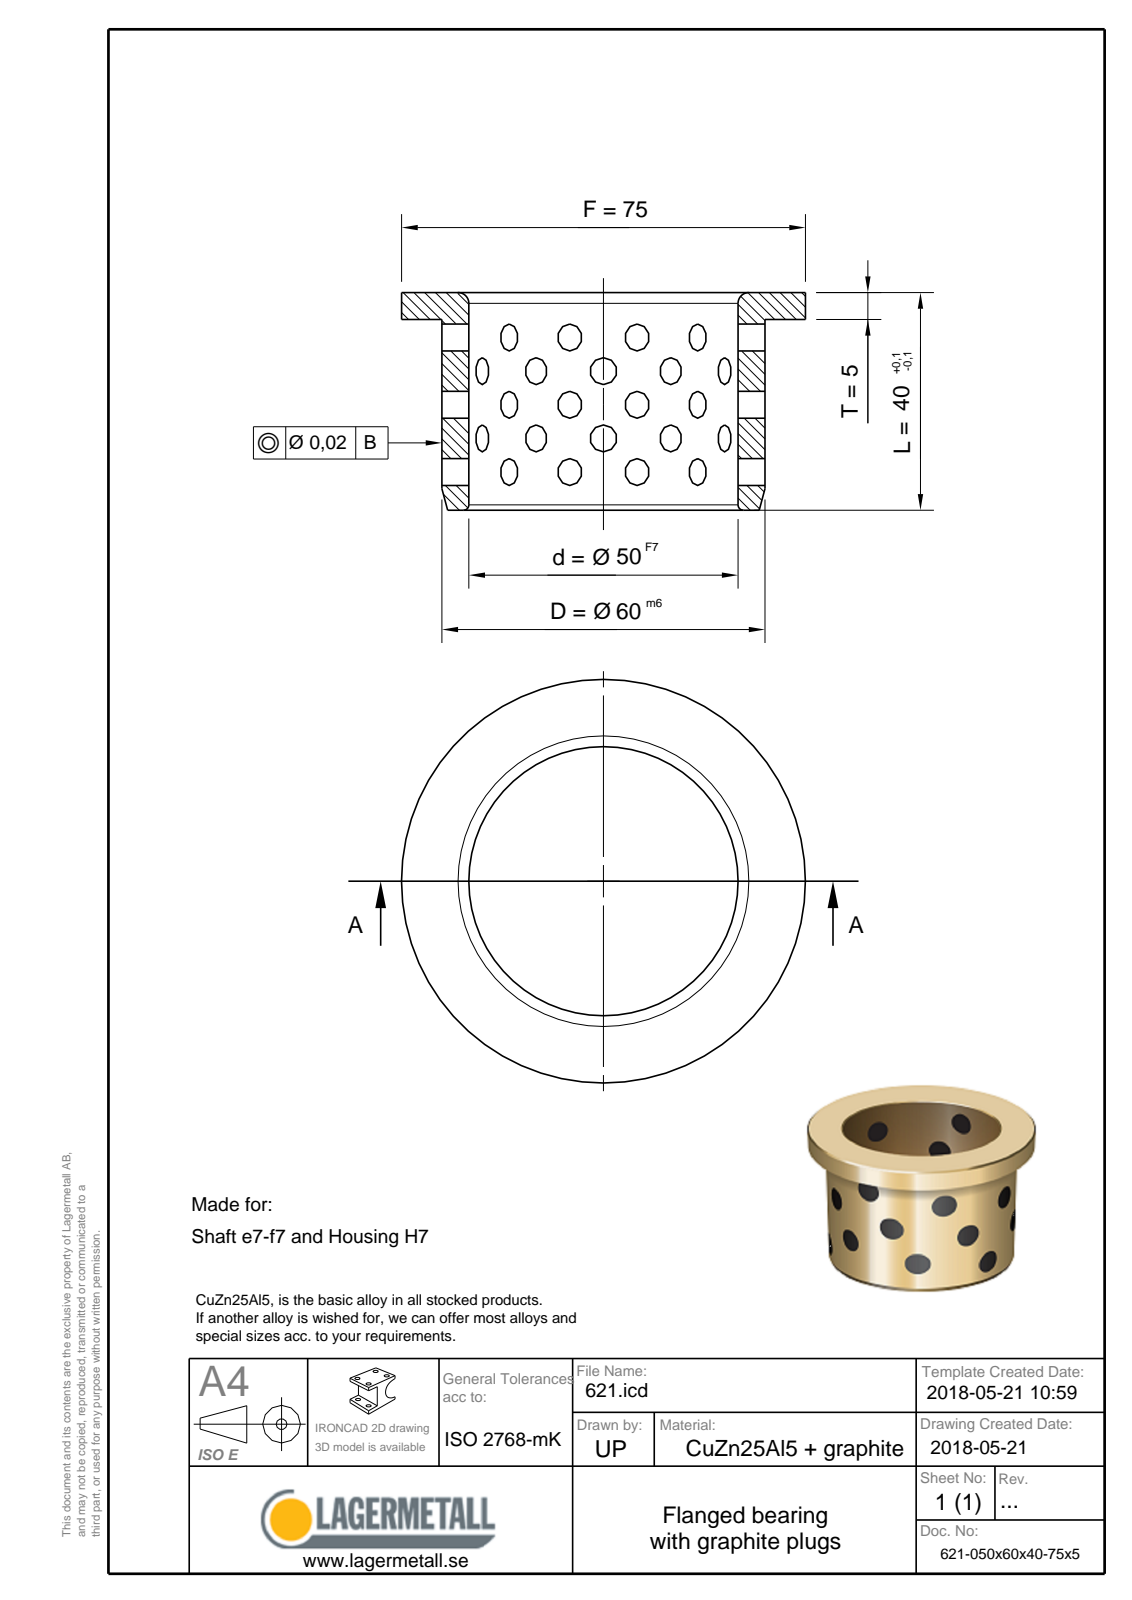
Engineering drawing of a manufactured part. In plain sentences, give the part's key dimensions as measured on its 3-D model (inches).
The part is named "621-050x60x40-75x5". Its 3-D file was written by "Spatial InterOp 3D (CONFIG_CONTROL_DESIGN)". It is 1 solid with 9 faces: 3 planar, 3 cylindrical and 3 other. Overall it measures 2.953 by 2.953 by 1.575 inches. Its volume is 2.564 cubic inches and its surface area 28.78 square inches. Round holes: 1 of diameter 1.969. Round bosses or shafts: 1 of diameter 2.953, 1 of diameter 2.362. The main face-to-face distances are 0.197, 1.378, 1.575.
